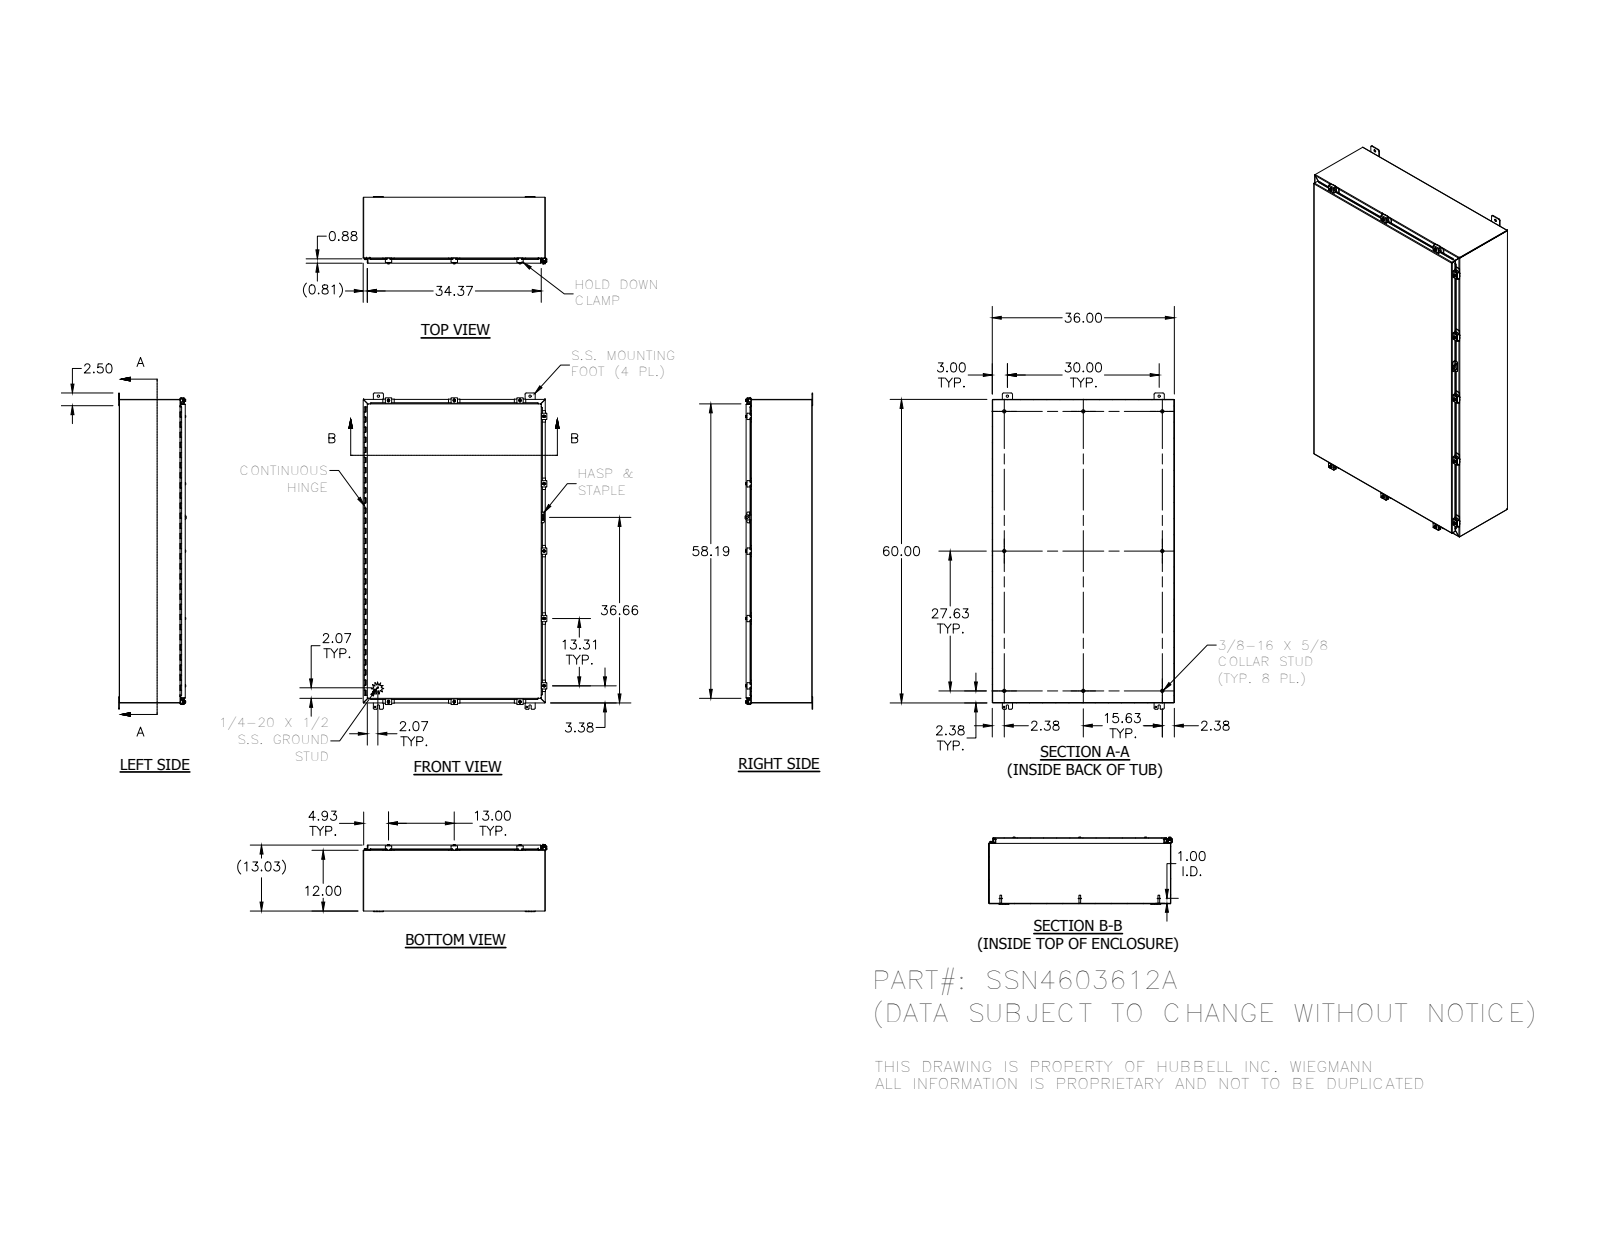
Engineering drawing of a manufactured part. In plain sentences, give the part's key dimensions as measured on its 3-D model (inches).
The part is named "30819; 58x34; HFW308001; SSN4603612A (+8 more)". Its 3-D file was written by "SolidWorks 2014 (AUTOMOTIVE_DESIGN)". It is 78 solids with 2976 faces: 1222 planar, 1307 cylindrical and 447 other. Overall it measures 62.5 by 36.311 by 13.355 inches. Its volume is 557 cubic inches and its surface area 14 810 square inches. Round holes: 11 of diameter 0.211, 11 of diameter 0.281, 11 of diameter 0.3, 4 of diameter 0.313, 4 of diameter 0.438, 1 of diameter 0.125, 1 of diameter 0.156, 1 of diameter 0.5. Round bosses or shafts: 13 of diameter 0.25, 11 of diameter 0.52, 11 of diameter 0.5, 11 of diameter 0.35, 8 of diameter 0.625, 8 of diameter 0.33, 1 of diameter 0.337, 1 of diameter 0.12. Partial cylindrical surfaces (rounded edges, fillets, slot ends): 129 of radius 0.03, 43 of radius 0.125, 39 of radius 0.25, 22 of radius 0.141, 21 of radius 0.031, 21 of radius 0.105, 20 of radius 0.062, 16 of radius 0.1. The main face-to-face distances are 0.074, 12.959, 12.885, 13.033, 35.926, 59.926, 35.852, 36, 11.926, 1.033. The hole center spacings are 1.593, 13, 30, 60, 61.018, 67.082, 13.313, 59.617.
